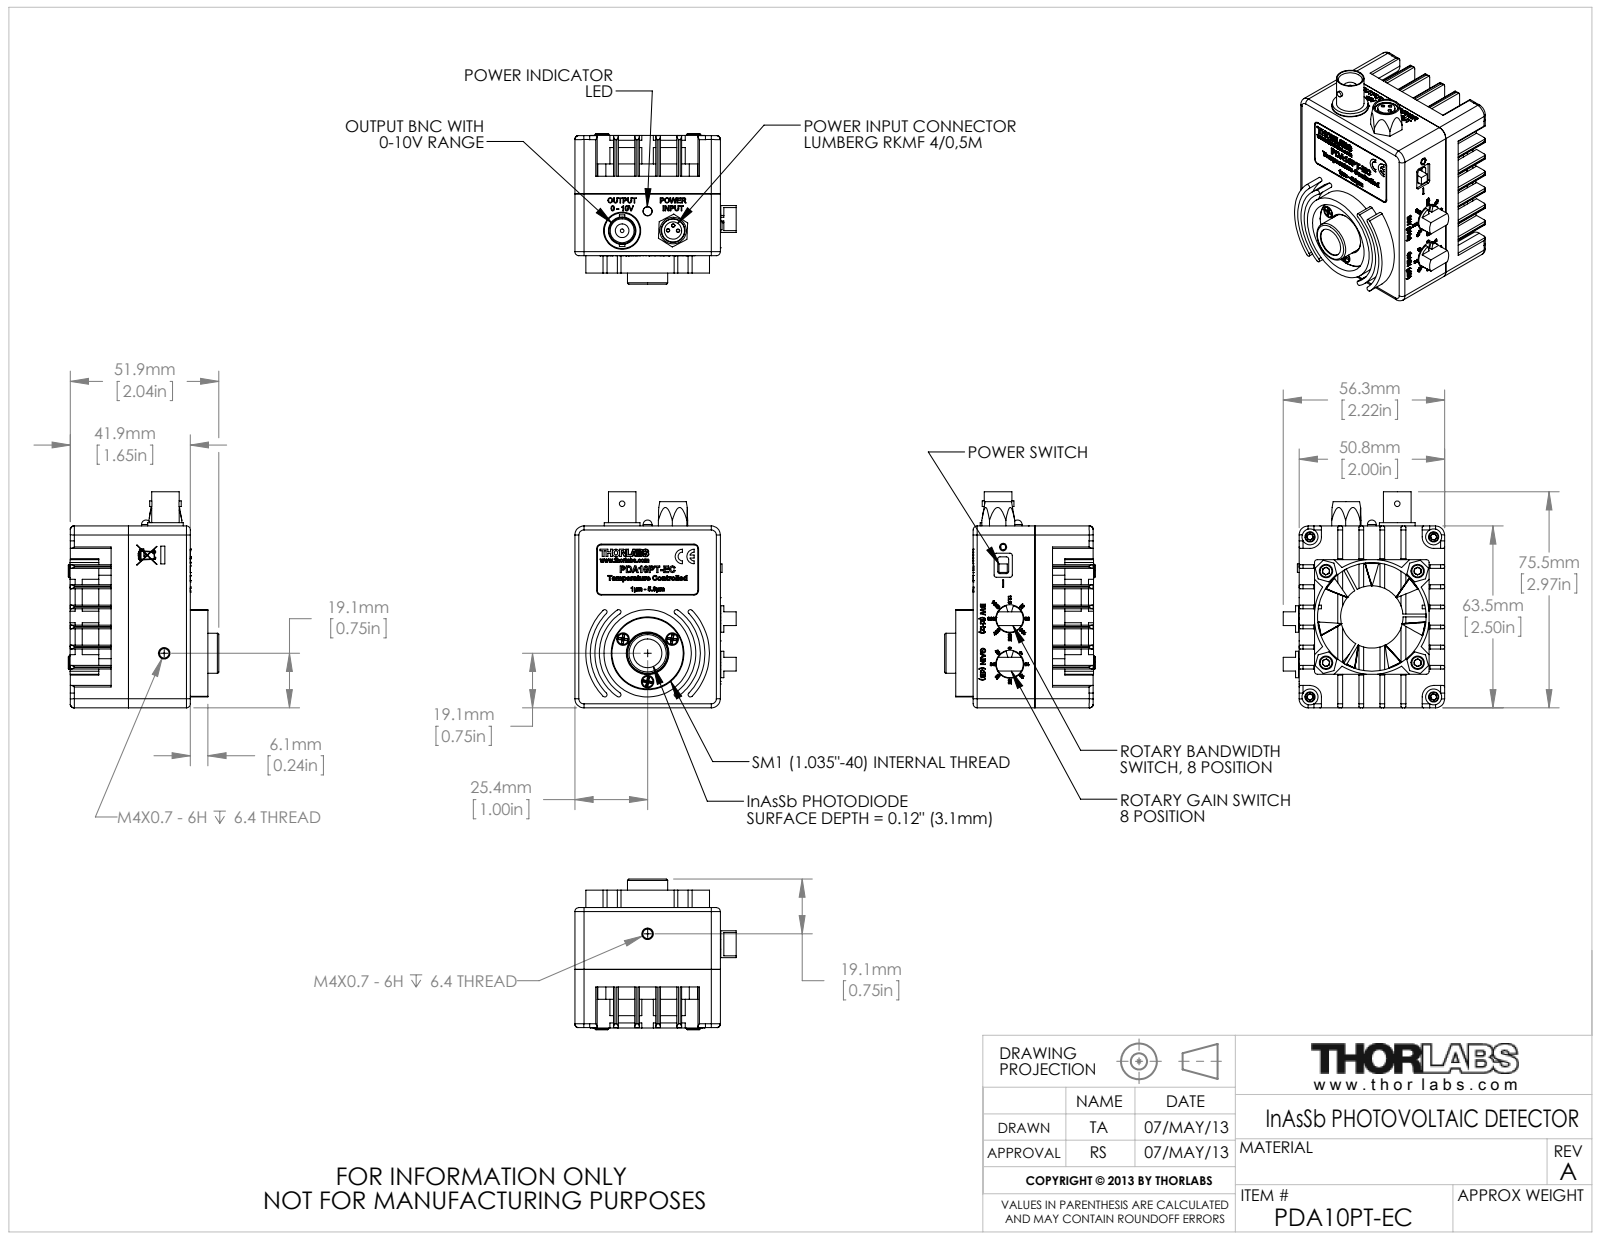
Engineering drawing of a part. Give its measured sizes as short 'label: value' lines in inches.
name: TTN012806-E0W
written by: SolidWorks 2012 (AUTOMOTIVE_DESIGN)
unit: in
bodies: 44 solids, 4293 faces (2356 planar, 758 cylindrical, 1179 other)
size: 2.971 × 2.218 × 2.07
volume: 4.033 in³; area: 96.53 in²
holes: 20× ⌀0.037, 11× ⌀0.086, 10× ⌀0.032, 9× ⌀0.096, 8× ⌀0.07, 7× ⌀0.05, 6× ⌀0.059, 6× ⌀0.063, 4× ⌀0.015, 4× ⌀0.089, 4× ⌀0.098, 4× ⌀0.112
bosses: 6× ⌀0.018, 4× ⌀0.183, 4× ⌀0.14, 4× ⌀0.112, 4× ⌀0.086, 3× ⌀0.37, 3× ⌀0.147, 2× ⌀0.139
rounds: 48× R0.02, 33× R0.008, 22× R0.1, 20× R0.004, 16× R0.031, 8× R0.055, 4× R0.014, 4× R0.039
face distances: 0.063, 0.3, 0.05, 0.24, 0.8, 0.29, 0.32, 0.85, 1.09, 0.56
hole spacings: 0.1, 0.224, 0.141, 0.317, 0.449, 0.069, 0.201, 0.35
